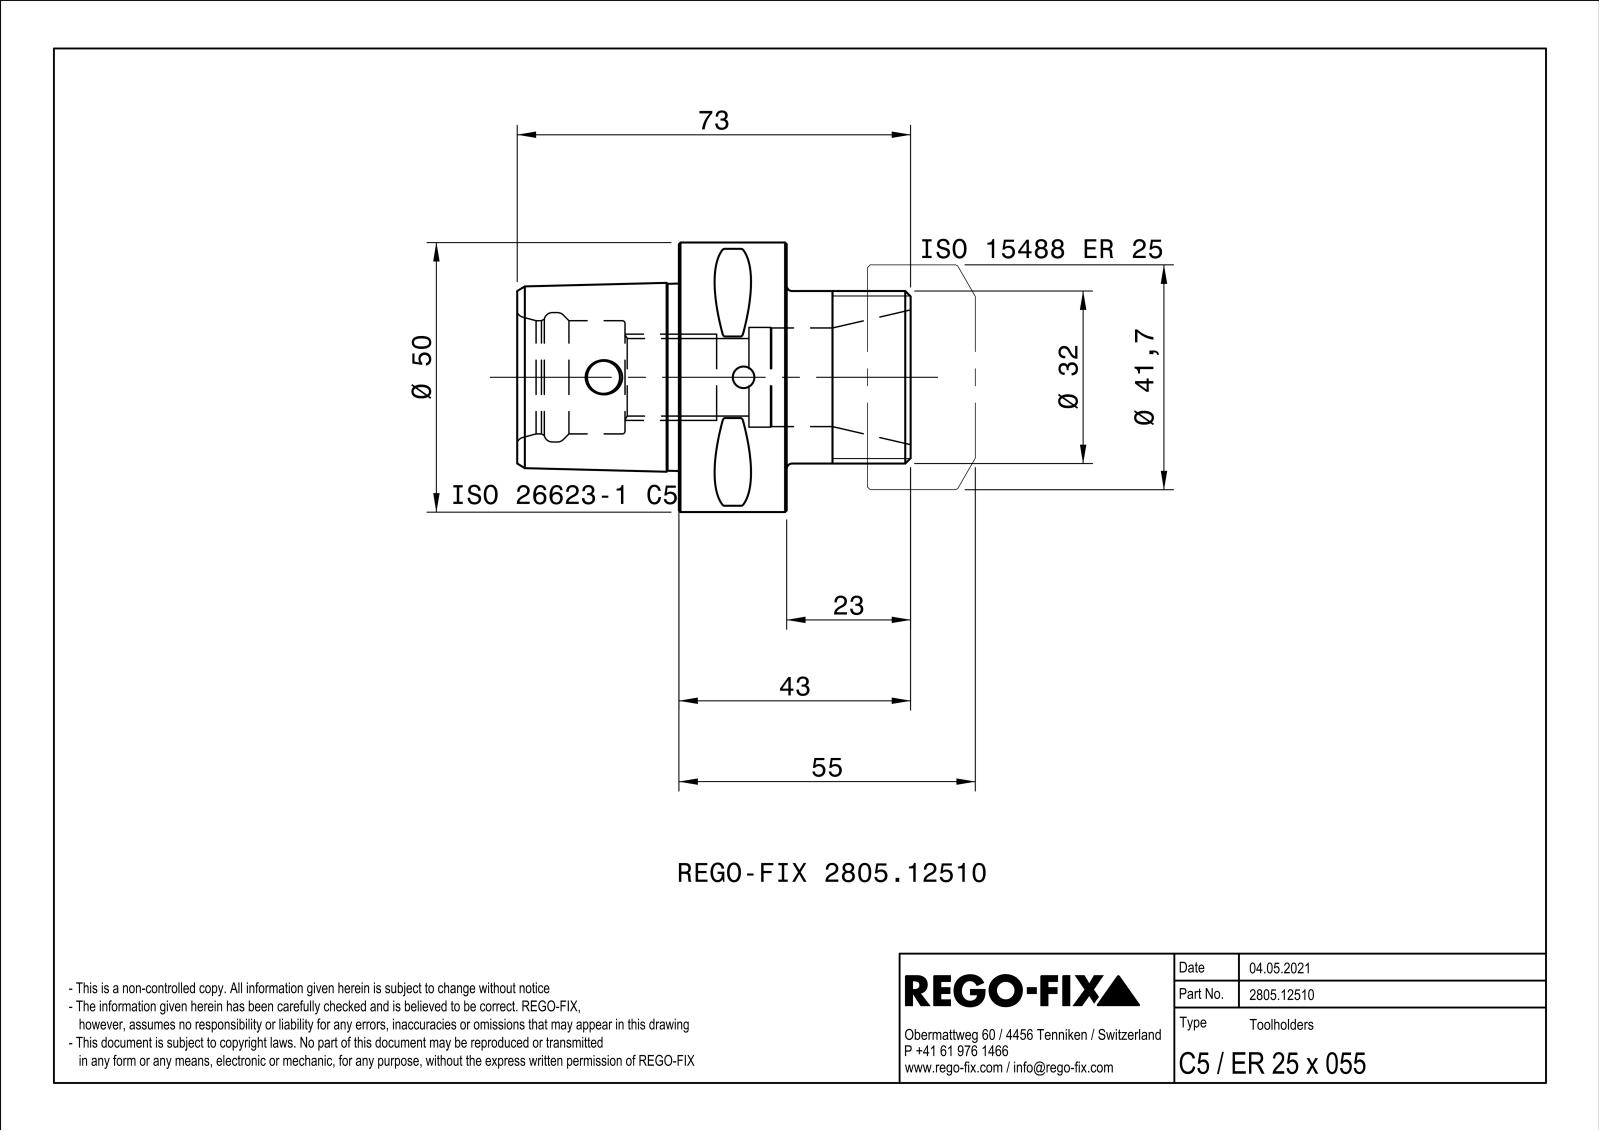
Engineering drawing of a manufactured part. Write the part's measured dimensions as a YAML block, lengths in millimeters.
part_name: "NOCUT"
step_written_by: "SIEMENS PLM Software Solid Edge ST10 (AUTOMOTIVE_DESIGN)"
units: millimeters
bodies: {solids: 1, faces: 96, planar: 21, cylindrical: 22, other: 53}
overall_size: [73, 50, 50]
volume: 62038
surface_area: 16533
round_holes:
  - {diameter: 4, count: 1}
  - {diameter: 6.1, count: 1}
  - {diameter: 14.38, count: 1}
  - {diameter: 18.3, count: 1}
  - {diameter: 18.5, count: 1}
  - {diameter: 21, count: 1}
  - {diameter: 24, count: 1}
round_bosses_or_shafts:
  - {diameter: 50, count: 1}
  - {diameter: 32, count: 1}
partial_cylinders:
  - {radius: 0.5, count: 8}
  - {radius: 4, count: 1}
face_to_face_distances: [20, 30, 50, 23, 43, 73, 19.18, 44.4, 53, 10]
hole_center_spacings: [26]
